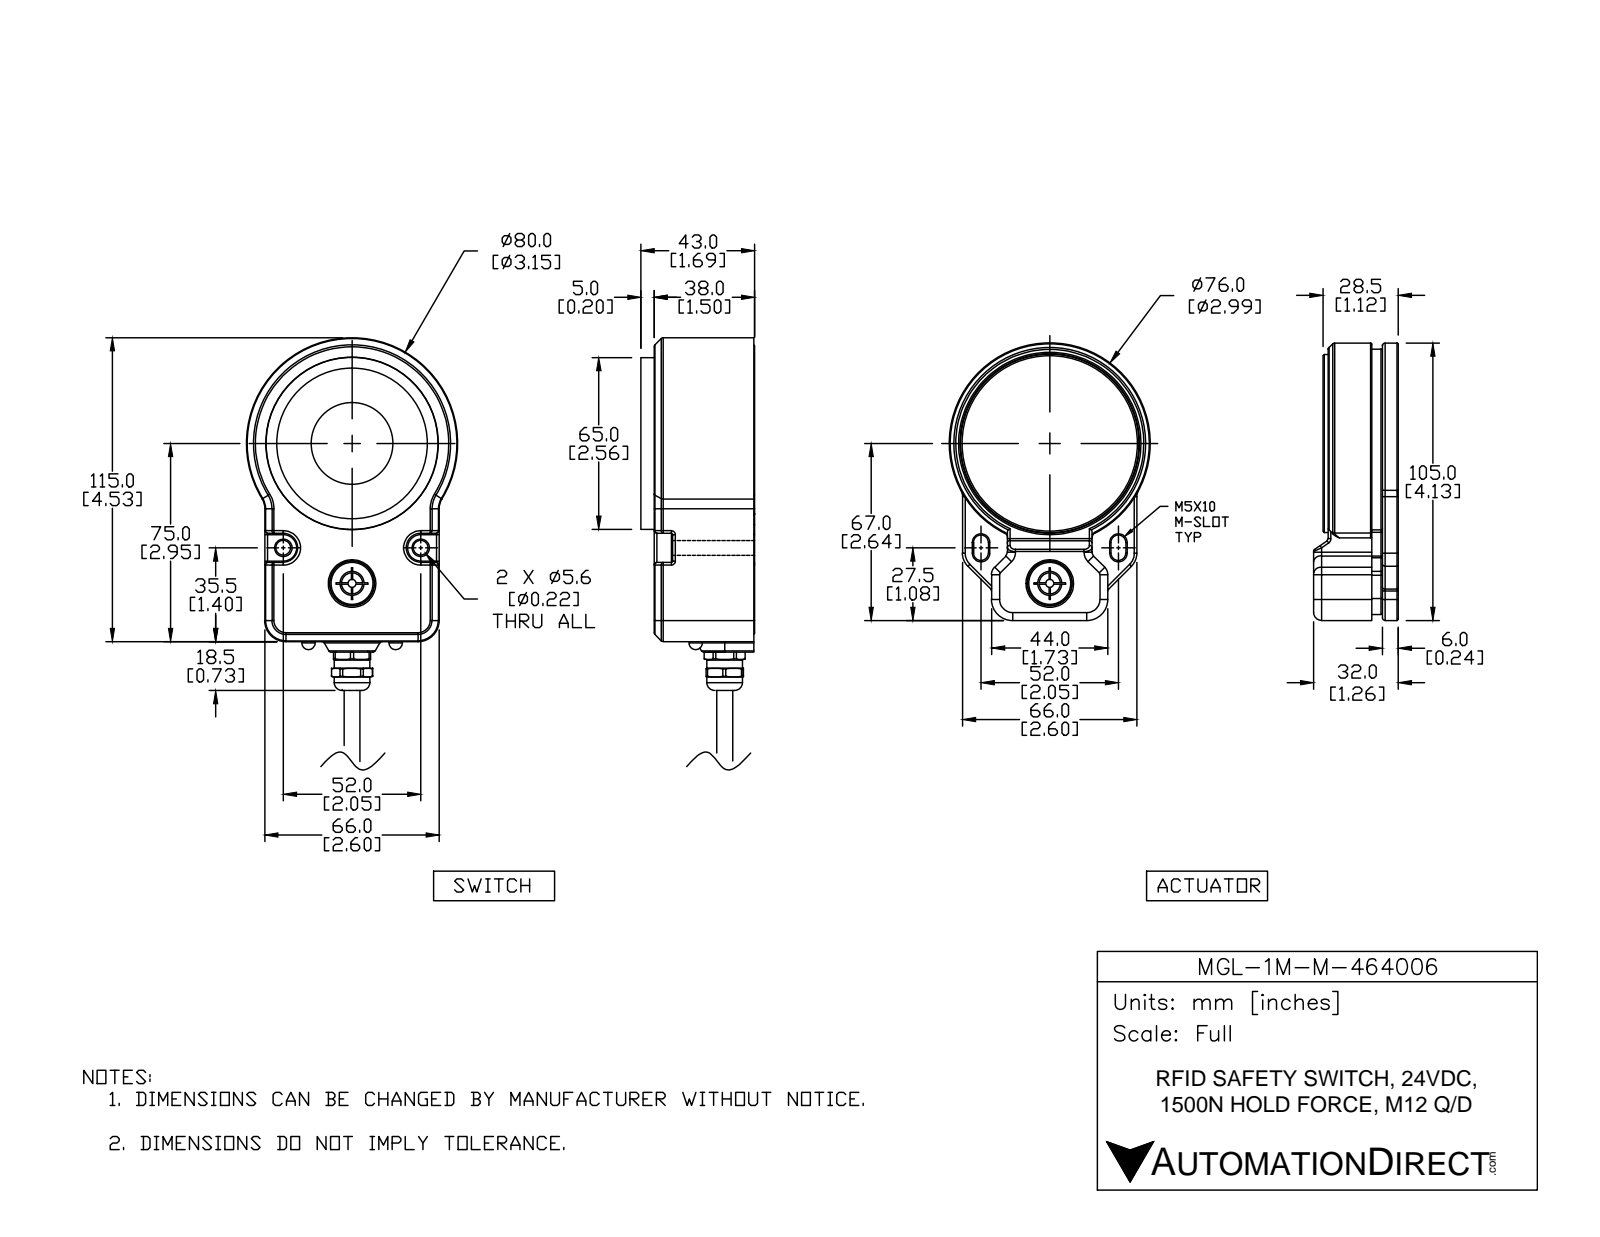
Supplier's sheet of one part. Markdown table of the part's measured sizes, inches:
| quantity | value |
| --- | --- |
| part name | MGL-1M-M-464006_1; MGL-1M-M-464006; MGL-1M-M-464006_2 |
| STEP written by | SolidWorks 2017 (AUTOMOTIVE_DESIGN) |
| units | inches |
| bodies | 19 solids, 1753 faces (428 planar, 743 cylindrical, 582 other) |
| overall size | 8.163 × 3.15 × 2.85 |
| volume | 19.31 in³ |
| surface area | 219.5 in² |
| round holes (diameter × count) | 0.098 × 8, 0.13 × 6, 0.197 × 6, 0.453 × 5, 0.157 × 3, 0.315 × 3, 0.354 × 3, 0.22 × 2, 0.276 × 2, 0.374 × 2, 0.465 × 2, 0.252 × 1 |
| round bosses / shafts (diameter × count) | 0.02 × 4, 0.079 × 3, 0.472 × 2, 0.228 × 2, 0.213 × 2, 0.047 × 2, 2.992 × 1, 2.811 × 1 |
| partial cylindrical surfaces (radius × count) | 0.02 × 186, 0.039 × 86, 0.079 × 26, 0.012 × 17, 0.118 × 13, 0.157 × 9, 0.217 × 8, 0.024 × 7 |
| main face-to-face distances | 0.315, 0.236, 2.299, 1.378, 0.118, 2.614, 0.413, 2.201, 2.85, 0.65 |
| hole center spacings | 1.392, 1.969, 0.984, 1.28, 1.537, 0.787, 1.364, 0.349 |
